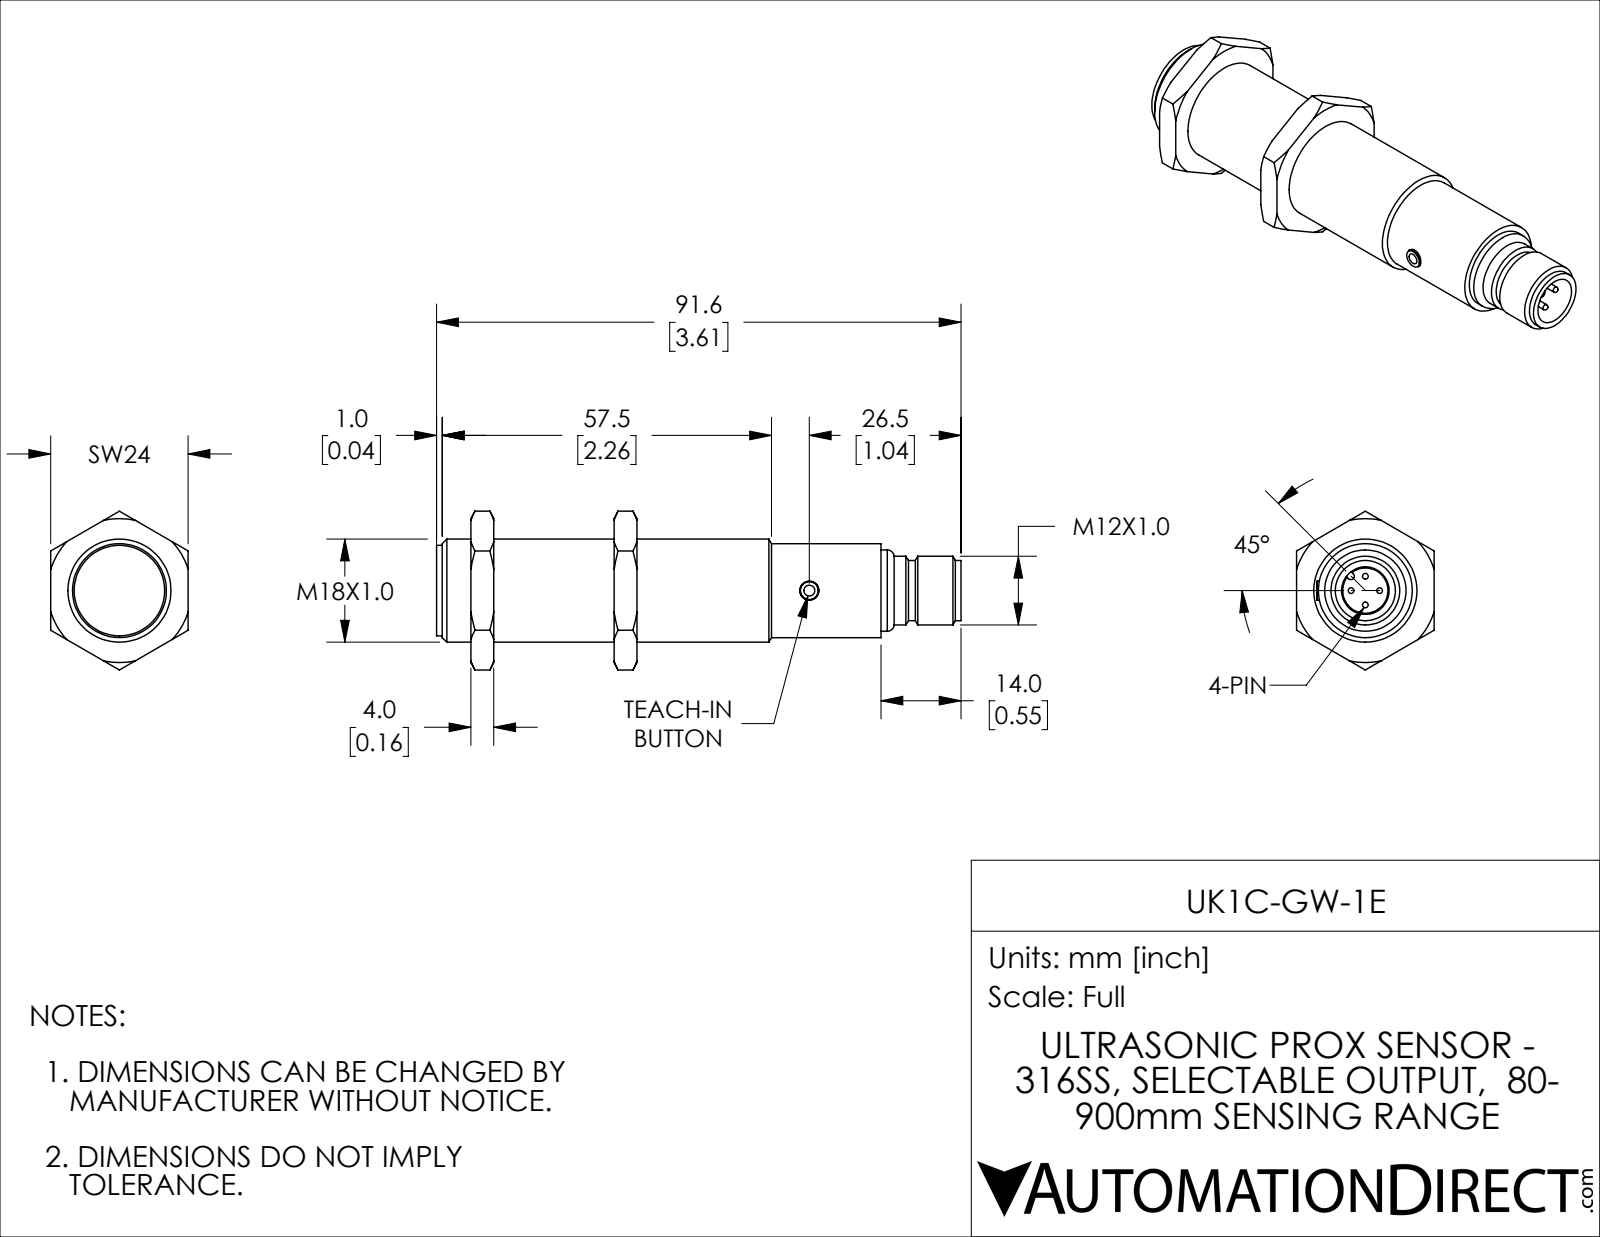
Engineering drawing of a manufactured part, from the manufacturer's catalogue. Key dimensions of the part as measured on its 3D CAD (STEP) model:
Part name (STEP PRODUCT): UK1C-GW-1E
STEP written by: SolidWorks 2018 (AUTOMOTIVE_DESIGN)
Units: inches
Bodies: 4 solids, 113 faces (27 planar, 35 cylindrical, 51 other)
Overall size (bounding box): 3.606 × 1.091 × 0.945
Volume: 1.338 in³ · Surface area: 11.97 in²
Round holes (diameter × count): ⌀0.13 ×1, ⌀0.327 ×1, ⌀0.709 ×1
Round bosses / shafts (diameter × count): ⌀0.039 ×4, ⌀0.646 ×1, ⌀0.622 ×1, ⌀0.559 ×1, ⌀0.472 ×1, ⌀0.413 ×1
Partial cylindrical surfaces — rounded edges, fillets, slot ends (radius × count): R0.024 ×1
Main face-to-face distances: 0.984, 0.157, 0.945, 1.142, 0.827, 0.236, 0.394, 1.22, 1.378, 3.055
